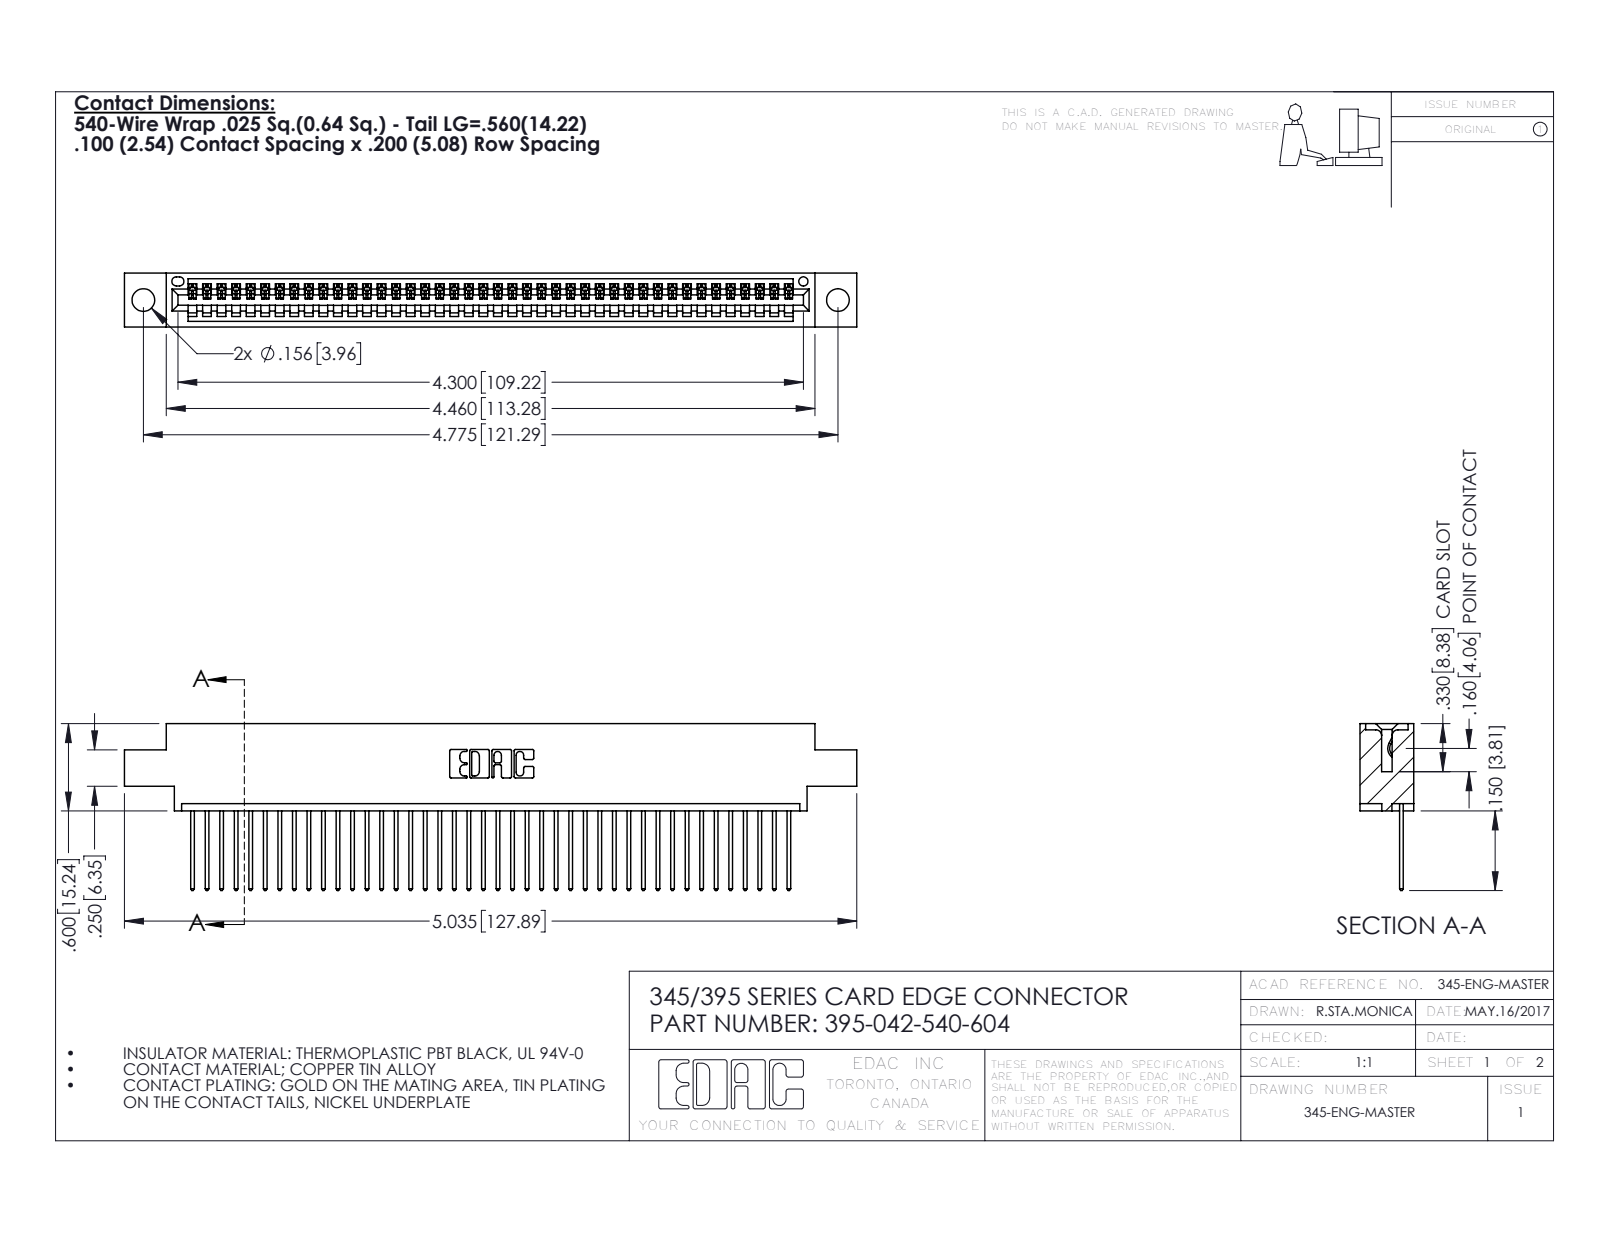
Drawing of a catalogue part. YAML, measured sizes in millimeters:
part_name: "345-292-001_345-293-140; 345 Part_0.170 Offset - 0.156 Dia-TH; 395-042-540-604"
step_written_by: "SolidWorks 2016 (CONFIG_CONTROL_DESIGN)"
units: millimeters
bodies: {solids: 43, faces: 2566, planar: 1764, cylindrical: 802, other: 0}
overall_size: [127.9, 29.1, 9.4]
volume: 12000
surface_area: 16300
round_holes:
  - {diameter: 4, count: 2}
  - {diameter: 1.6, count: 1}
partial_cylinders:
  - {radius: 0.2, count: 84}
  - {radius: 0.3, count: 84}
  - {radius: 0.3, count: 22}
  - {radius: 0.2, count: 6}
  - {radius: 0.8, count: 6}
  - {radius: 0.7, count: 3}
  - {radius: 0.8, count: 2}
  - {radius: 1, count: 2}
face_to_face_distances: [7.6, 1.8, 9.4, 2.5, 6.9, 0.6, 5.1, 5.7, 4.4, 3.8]
hole_center_spacings: [6.9, 115.3, 121.3]
